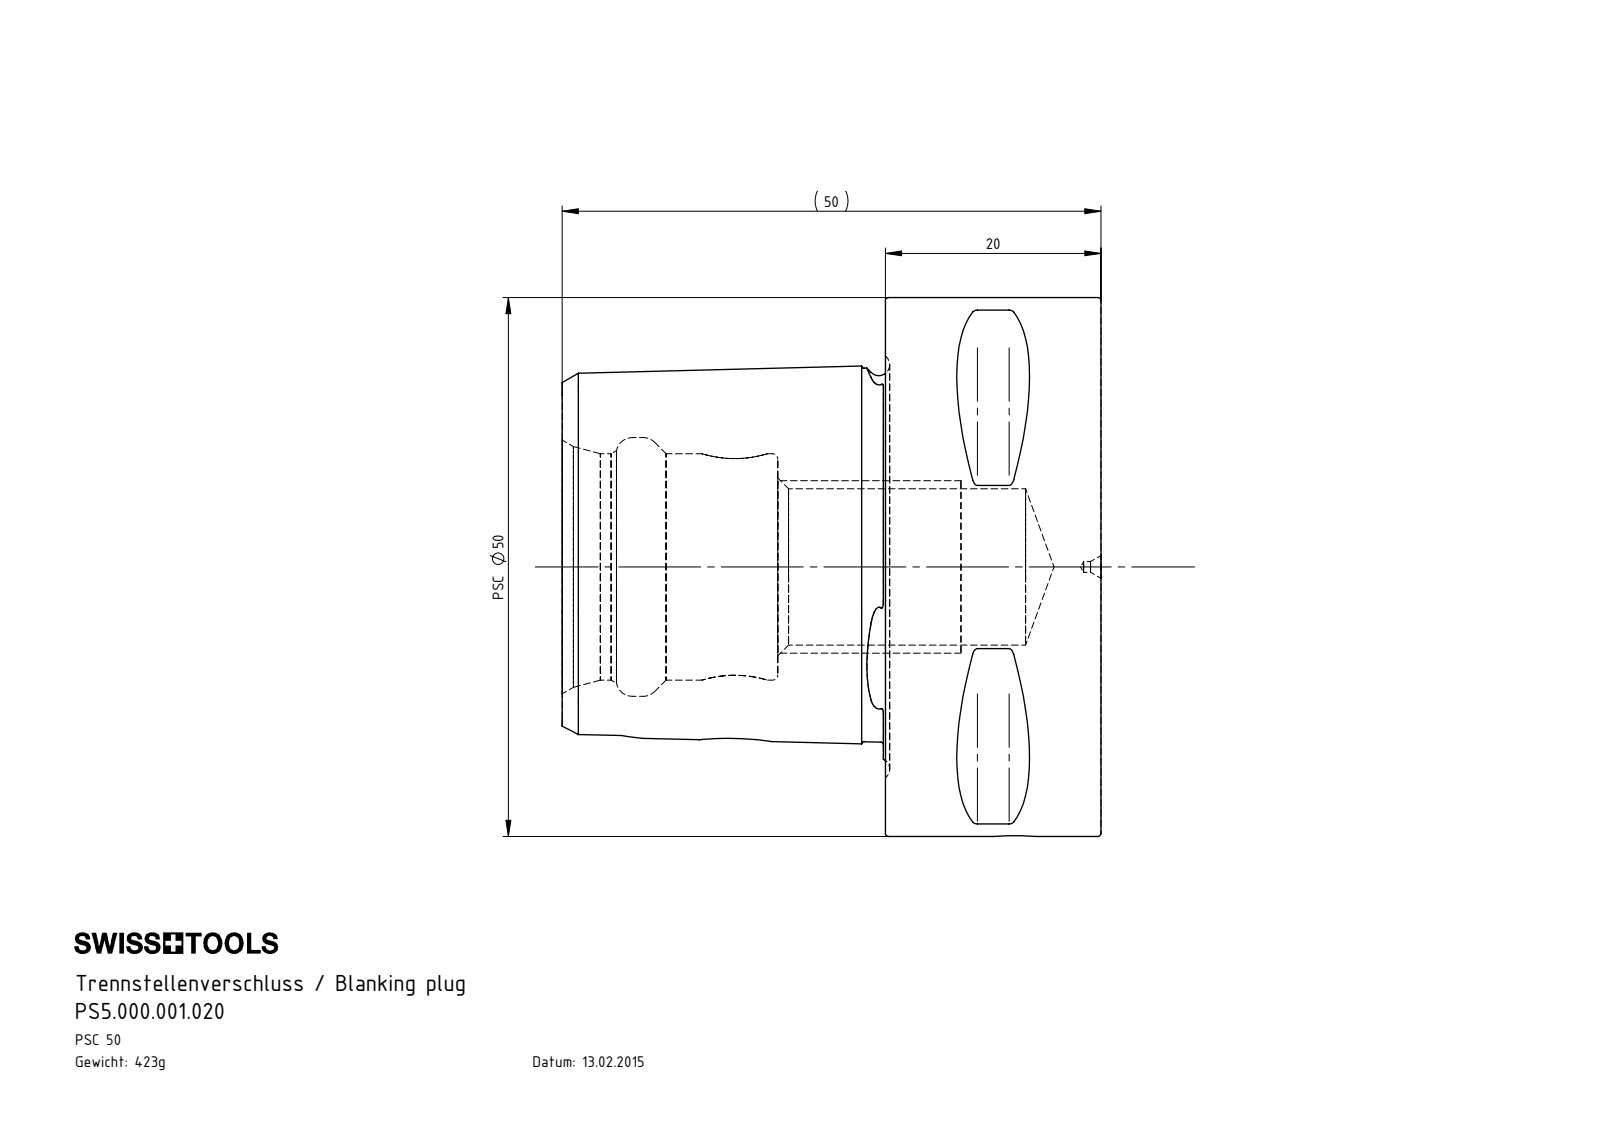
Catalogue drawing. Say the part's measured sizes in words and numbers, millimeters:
The part is named "PS5.000.001.020". Its 3-D file was written by "SolidWorks 2017 (AUTOMOTIVE_DESIGN)". It is 1 solid with 87 faces: 19 planar, 18 cylindrical and 50 other. Overall it measures 50 by 50 by 50 millimeters. Its volume is 53 901 cubic millimeters and its surface area 12 901 square millimeters. Round holes: 1 of diameter 1, 1 of diameter 4, 1 of diameter 6.1, 1 of diameter 14.5, 1 of diameter 21, 1 of diameter 24. Round bosses or shafts: 1 of diameter 50. Partial cylindrical surfaces (rounded edges, fillets, slot ends): 8 of radius 0.5, 1 of radius 4. The main face-to-face distances are 20, 30, 50, 19.18, 44.4, 10, 29.8, 9.8, 20.2. The hole center spacings are 26.
